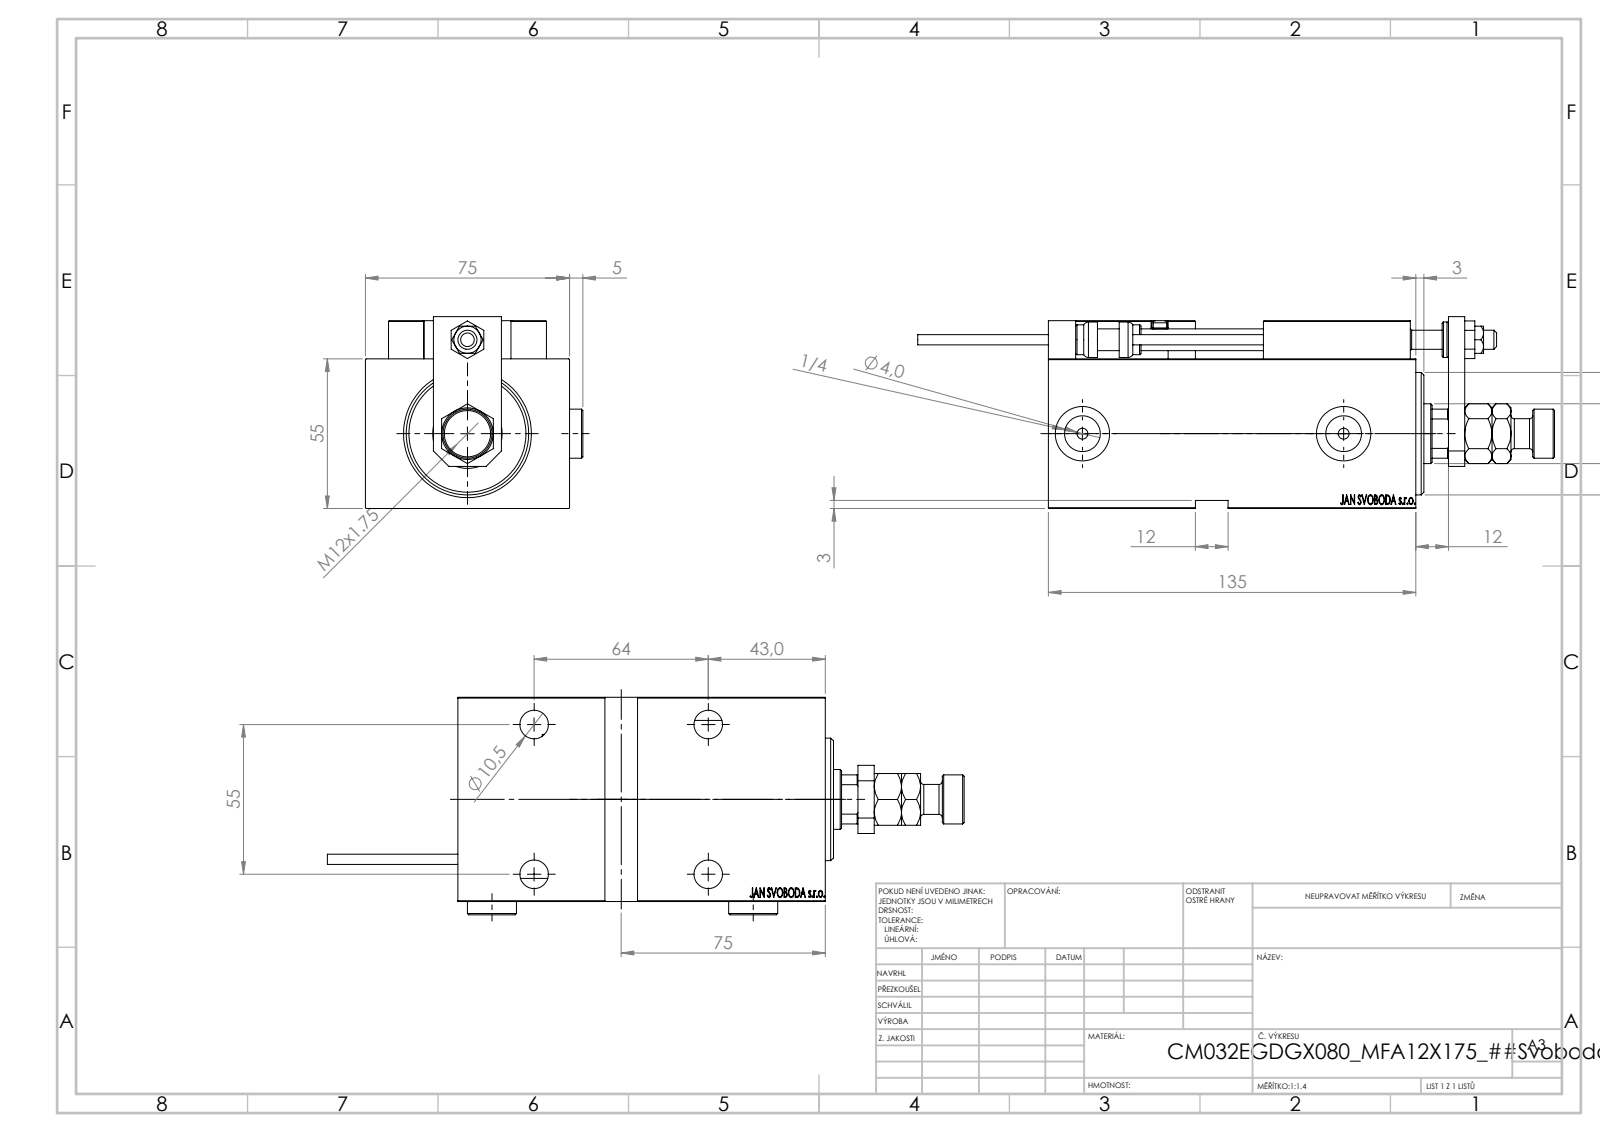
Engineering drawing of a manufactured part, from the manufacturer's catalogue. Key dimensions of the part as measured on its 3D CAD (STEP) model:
Part name (STEP PRODUCT): V450CM_VC_B; SWITCH DIM B,W; V450CM_E_Body; KONCOVKA (+8 more)
STEP written by: SolidWorks 2019 (CONFIG_CONTROL_DESIGN)
Units: millimetres
Bodies: 27 solids, 1398 faces (621 planar, 200 cylindrical, 577 other)
Overall size (bounding box): 234 × 79.9 × 70.5
Volume: 555 455 mm³ · Surface area: 115 752 mm²
Round holes (diameter × count): ⌀4 ×6, ⌀8 ×5, ⌀10.5 ×5, ⌀16.5 ×5, ⌀3.2 ×4, ⌀5 ×2, ⌀13.16 ×2, ⌀20 ×2, ⌀7 ×1, ⌀22 ×1, ⌀25.5 ×1, ⌀32 ×1
Round bosses / shafts (diameter × count): ⌀18 ×3, ⌀11 ×2, ⌀5 ×2, ⌀3.8 ×2, ⌀34 ×1, ⌀13 ×1
Partial cylindrical surfaces — rounded edges, fillets, slot ends (radius × count): R0.3 ×30, R3 ×2, R10.5 ×1
Main face-to-face distances: 55, 75, 3, 69, 10, 14, 135, 12, 5, 25
Hole centre spacings: 11.37, 20, 28.9, 29.59, 29.69, 36.06, 40.03, 42.19
